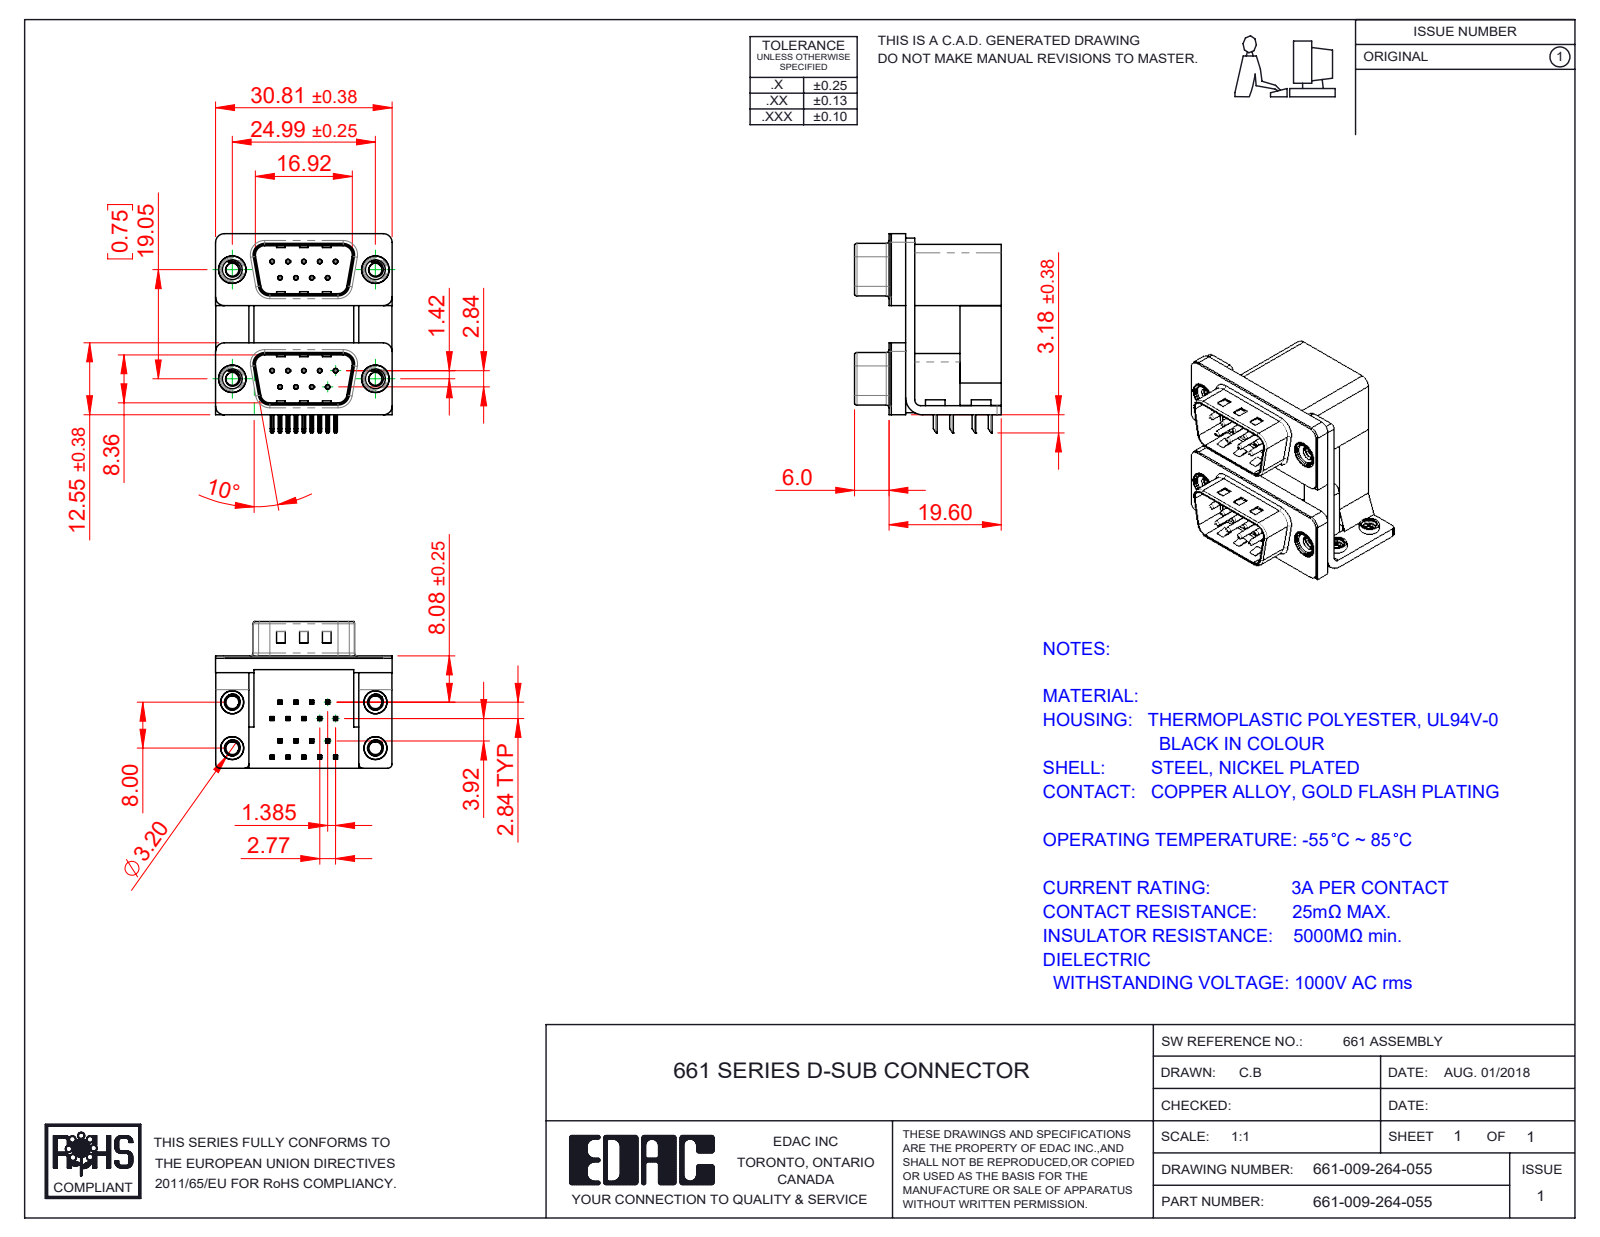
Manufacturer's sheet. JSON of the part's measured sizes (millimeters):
{"part_name": "661 Mounting Bracket_ThruM; 661 4-40 Threaded Board Mount; 661 Contact Top Lower; 661 Housing Upper_09 Contacts M (+8 more)", "step_written_by": "SolidWorks 2020 (CONFIG_CONTROL_DESIGN)", "units": "millimeters", "bodies": {"solids": 33, "faces": 2088, "planar": 1164, "cylindrical": 670, "other": 254}, "overall_size": [34.78, 30.81, 25.6], "volume_mm3": 10324, "surface_area_mm2": 12079, "round_holes": [[0.35, 18], [0.8, 18], [2.26, 8], [2.75, 4], [3.2, 4], [3.5, 4], [4, 4], [4.8, 4], [5, 4]], "round_bosses_or_shafts": [[0.75, 18], [4.9, 4], [4.75, 4], [4, 4], [3.9, 4], [3.4, 4]], "partial_cylinders_radius": [[0.25, 72], [0.12, 36], [0.5, 16], [1.5, 14], [0.75, 8], [0.9, 8], [1.6, 8], [2, 8]], "face_to_face_distances": [0.4, 2.5, 19.05, 16.7, 19.2, 10.69, 7.2, 9.5, 12, 1.6], "hole_center_spacings": [3.16, 2.77, 19.25, 19.05, 5.54, 19.84, 16.27, 21.93]}
